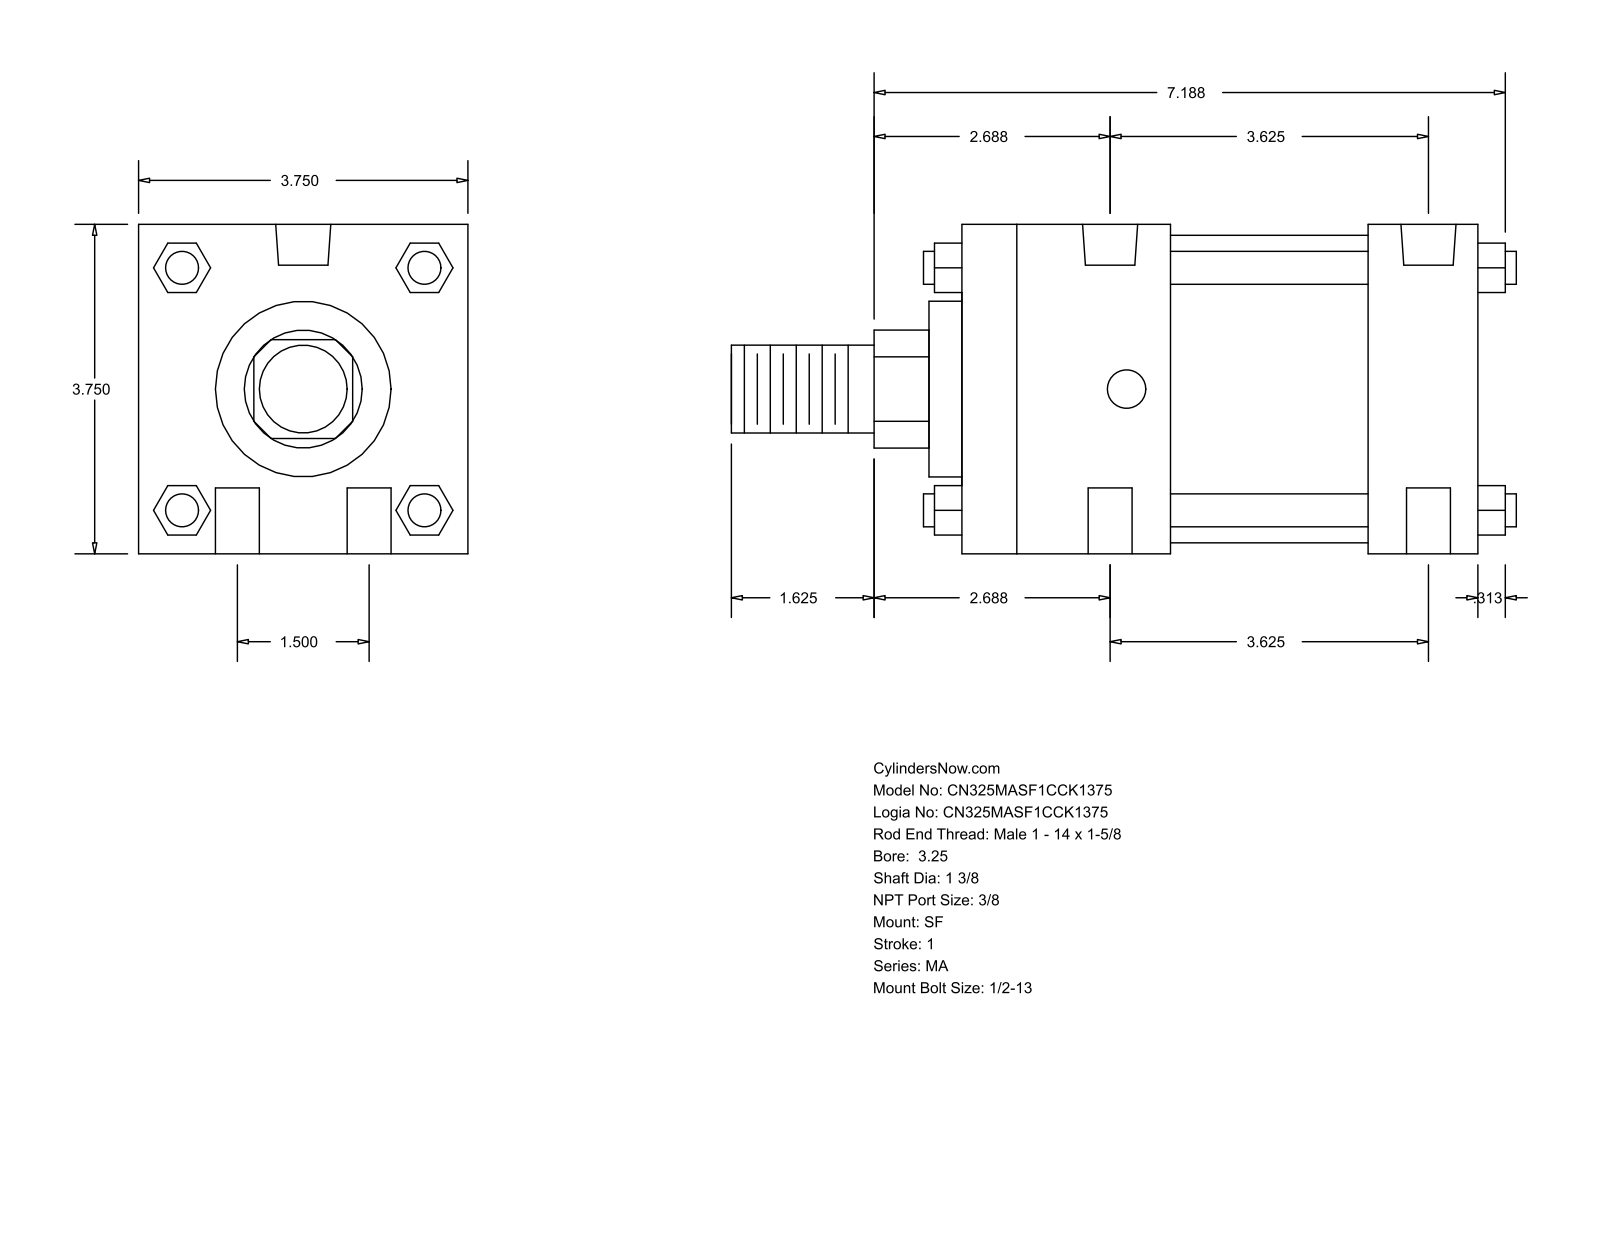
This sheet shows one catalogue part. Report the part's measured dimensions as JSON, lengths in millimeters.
{"part_name": "MA_SF__0325_1.375", "step_written_by": "GSSL Pune (CONFIG_CONTROL_DESIGN)", "units": "millimeters", "bodies": {"solids": 0, "faces": 124, "planar": 94, "cylindrical": 30, "other": 0}, "overall_size": [227.01, 95.25, 95.25], "round_holes": [[12.7, 4], [11.11, 2], [15.93, 2]], "round_bosses_or_shafts": [[9.53, 4], [88.9, 1], [50.8, 1], [34.92, 1], [25.4, 1]], "partial_cylinders_radius": [[17.06, 1]], "face_to_face_distances": [95.24, 149.22, 117.48, 31.74, 60.32, 57.16, 88.9, 9.52, 69.84, 127], "hole_center_spacings": [19.05, 94.03, 92.08, 38.1, 99.65, 82.54]}
